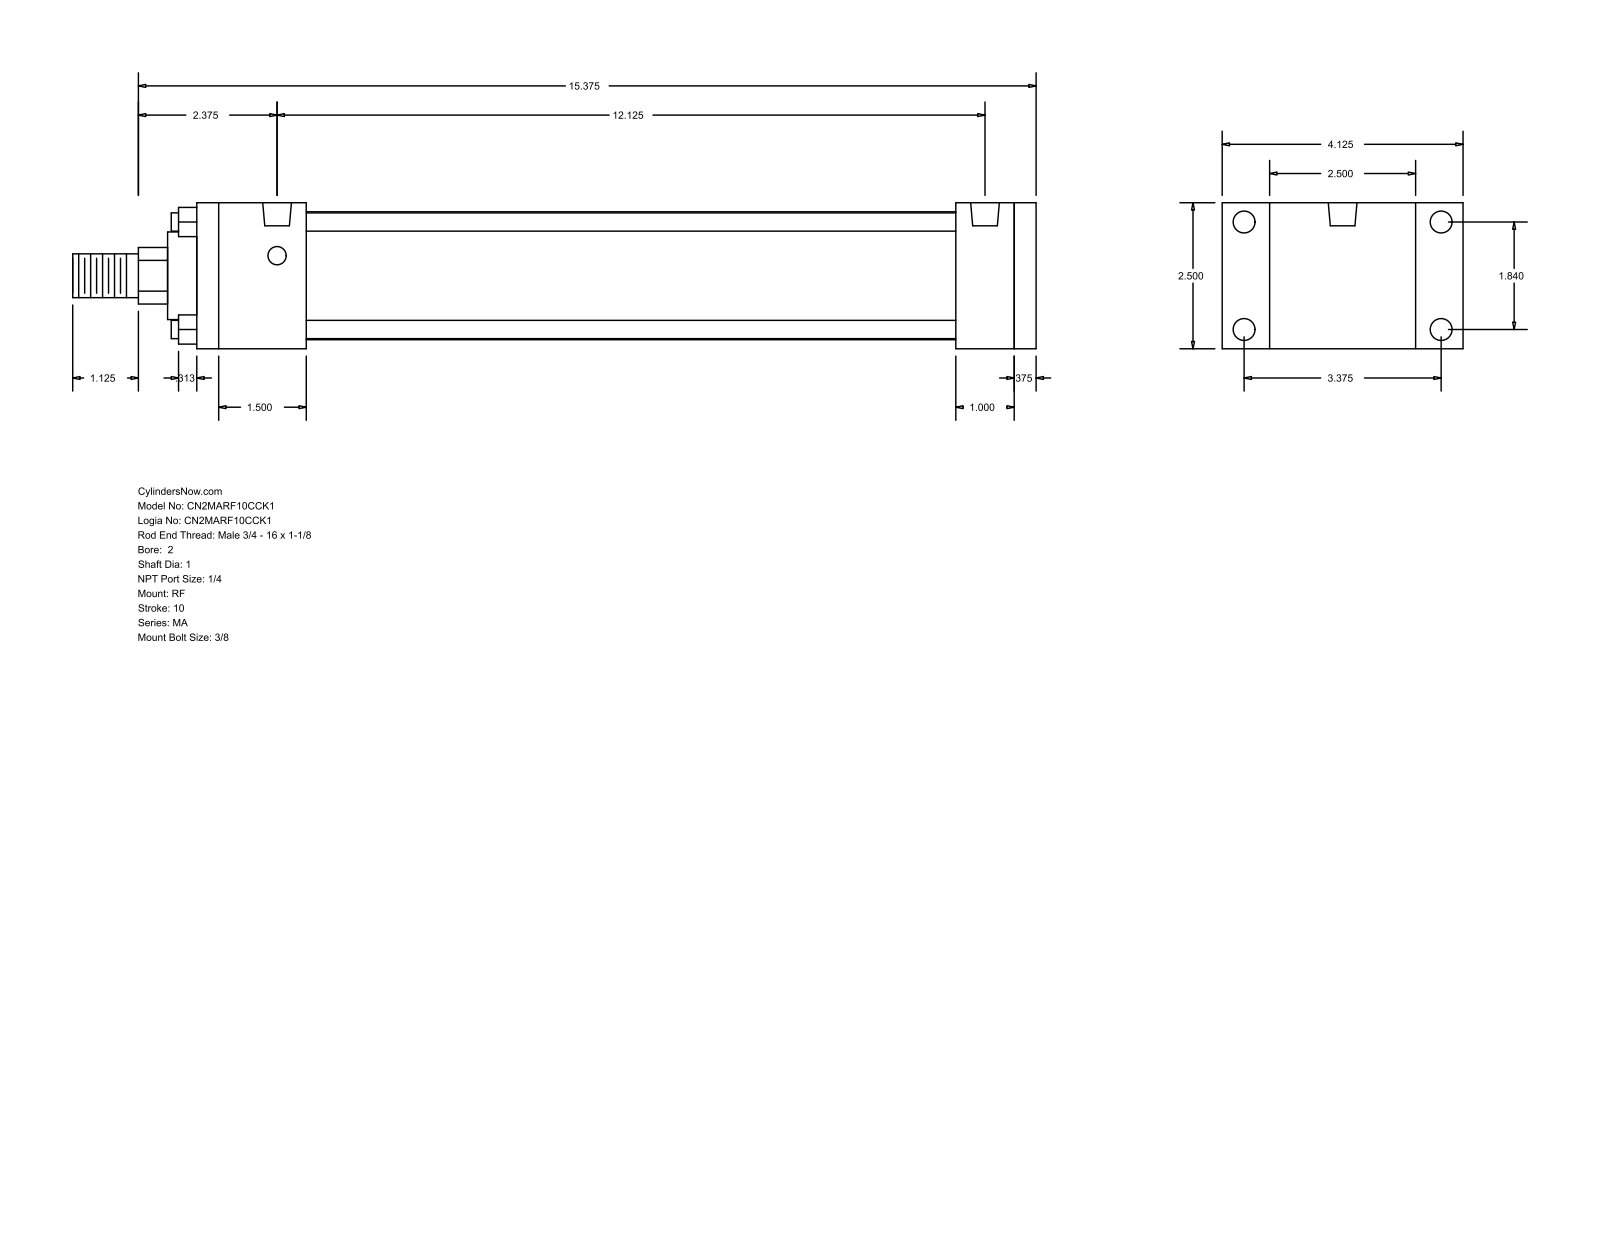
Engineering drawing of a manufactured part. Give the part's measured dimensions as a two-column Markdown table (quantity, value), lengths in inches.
| quantity | value |
| --- | --- |
| part name | MA_RF__0200_1 |
| STEP written by | GSSL Pune (CONFIG_CONTROL_DESIGN) |
| units | inches |
| bodies | 0 solids, 92 faces (64 planar, 28 cylindrical, 0 other) |
| overall size | 16.5 × 4.125 × 2.5 |
| round holes (diameter × count) | 0.313 × 4, 0.375 × 4, 0.492 × 2 |
| round bosses / shafts (diameter × count) | 0.313 × 4, 2.19 × 1, 1.5 × 1, 1 × 1, 0.75 × 1 |
| partial cylindrical surfaces (radius × count) | 0.484 × 1 |
| main face-to-face distances | 2.5, 14, 0.375, 14.375, 1, 0.813, 0.5, 1.875, 12.125, 12.5 |
| hole center spacings | 1.84, 3.375, 3.844, 12.125 |
